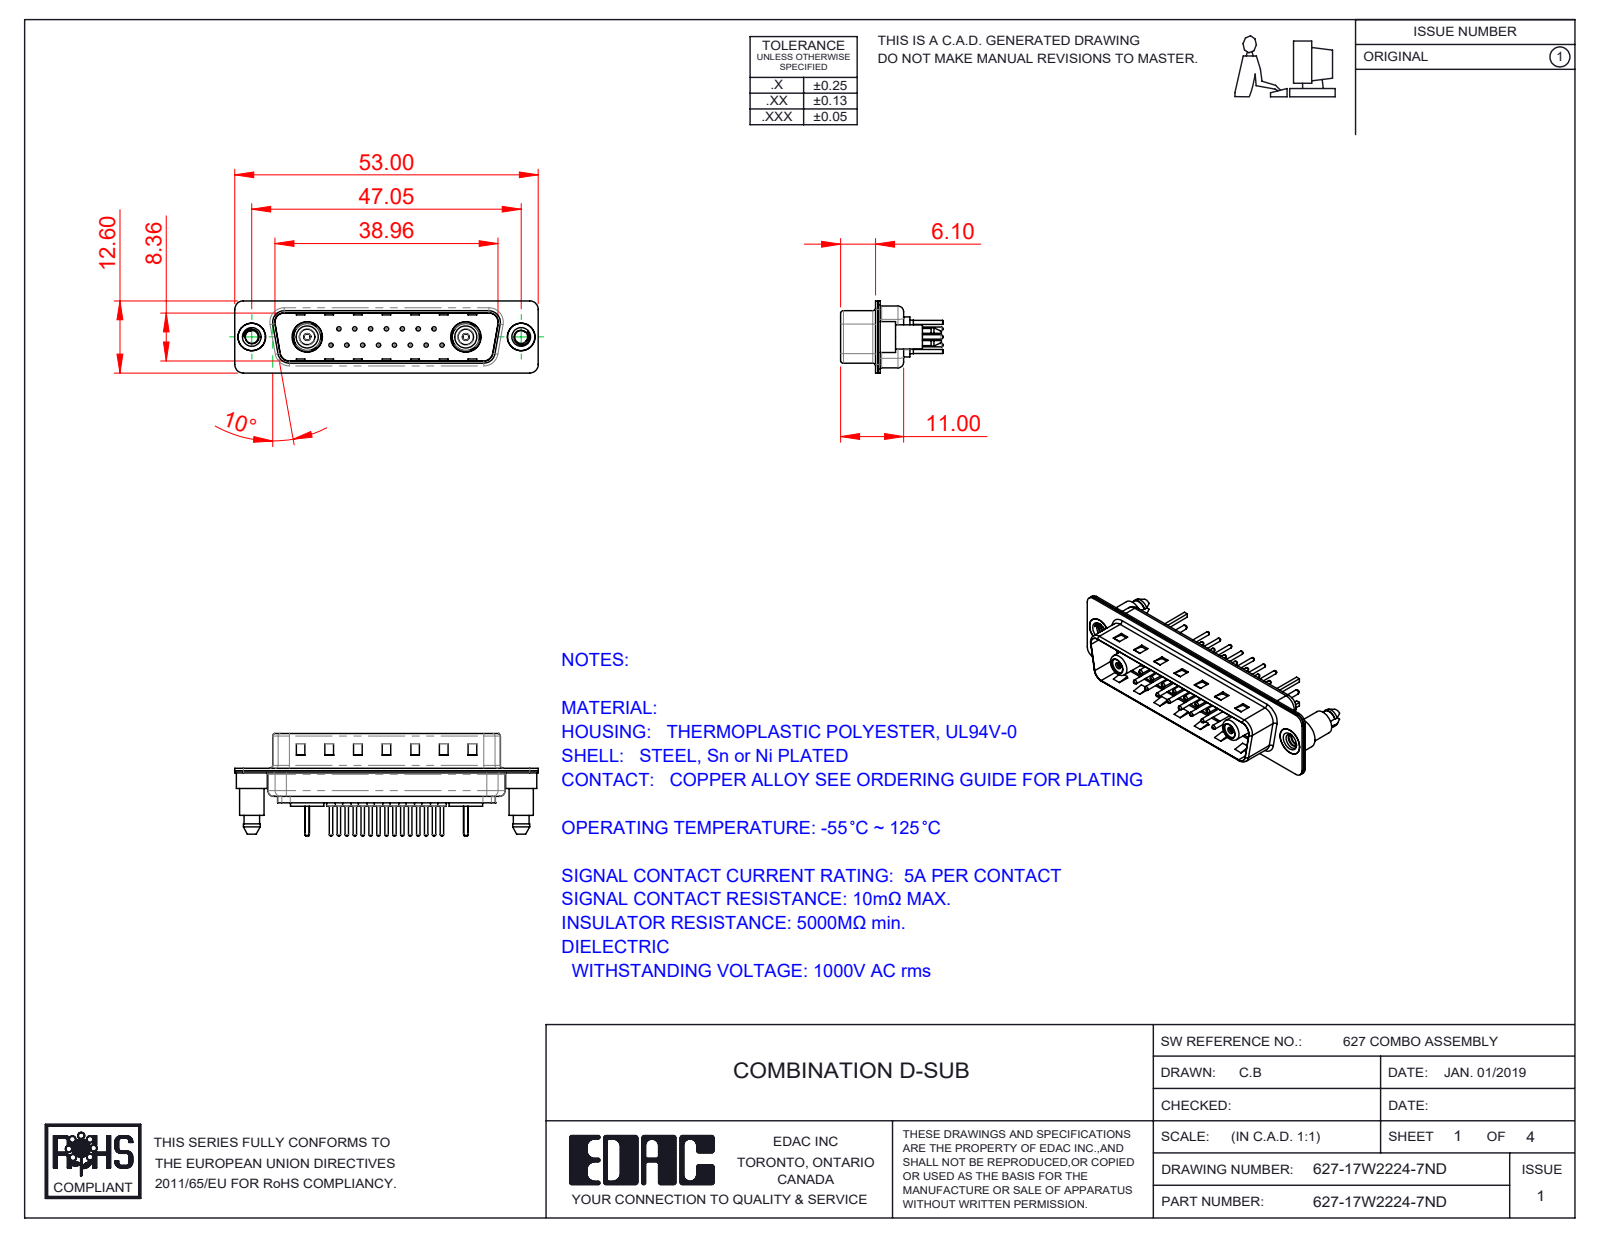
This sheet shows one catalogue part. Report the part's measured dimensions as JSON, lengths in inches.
{"part_name": "Co-Ax Jack Assy_S; Socket_Str; 627Combo Housing_17W2; 627Combo Contact Row 1_24 (+8 more)", "step_written_by": "SolidWorks 2016 (CONFIG_CONTROL_DESIGN)", "units": "inches", "bodies": {"solids": 30, "faces": 1211, "planar": 386, "cylindrical": 481, "other": 344}, "overall_size": [2.087, 0.705, 0.496], "volume_in3": 0.177, "surface_area_in2": 12.3, "round_holes": [[0.063, 17], [0.03, 15], [0.079, 15], [0.043, 2], [0.047, 2], [0.059, 2], [0.089, 2], [0.098, 2], [0.106, 2], [0.134, 2], [0.157, 2], [0.189, 2]], "round_bosses_or_shafts": [[0.059, 15], [0.024, 15], [0.23, 2], [0.213, 2], [0.205, 2], [0.193, 2], [0.189, 2], [0.186, 2]], "partial_cylinders_radius": [[0.059, 18], [0.079, 12], [0.063, 10], [0.02, 8], [0.01, 4], [0.024, 4], [0.026, 4], [0.035, 4]], "face_to_face_distances": [0.016, 0.032, 0.377, 0.345, 0.205, 0.059, 0.236, 0.031, 0.22, 0.048], "hole_center_spacings": [0.124, 0.109, 0.218, 0.327, 0.198, 0.295, 0.436, 0.198]}
